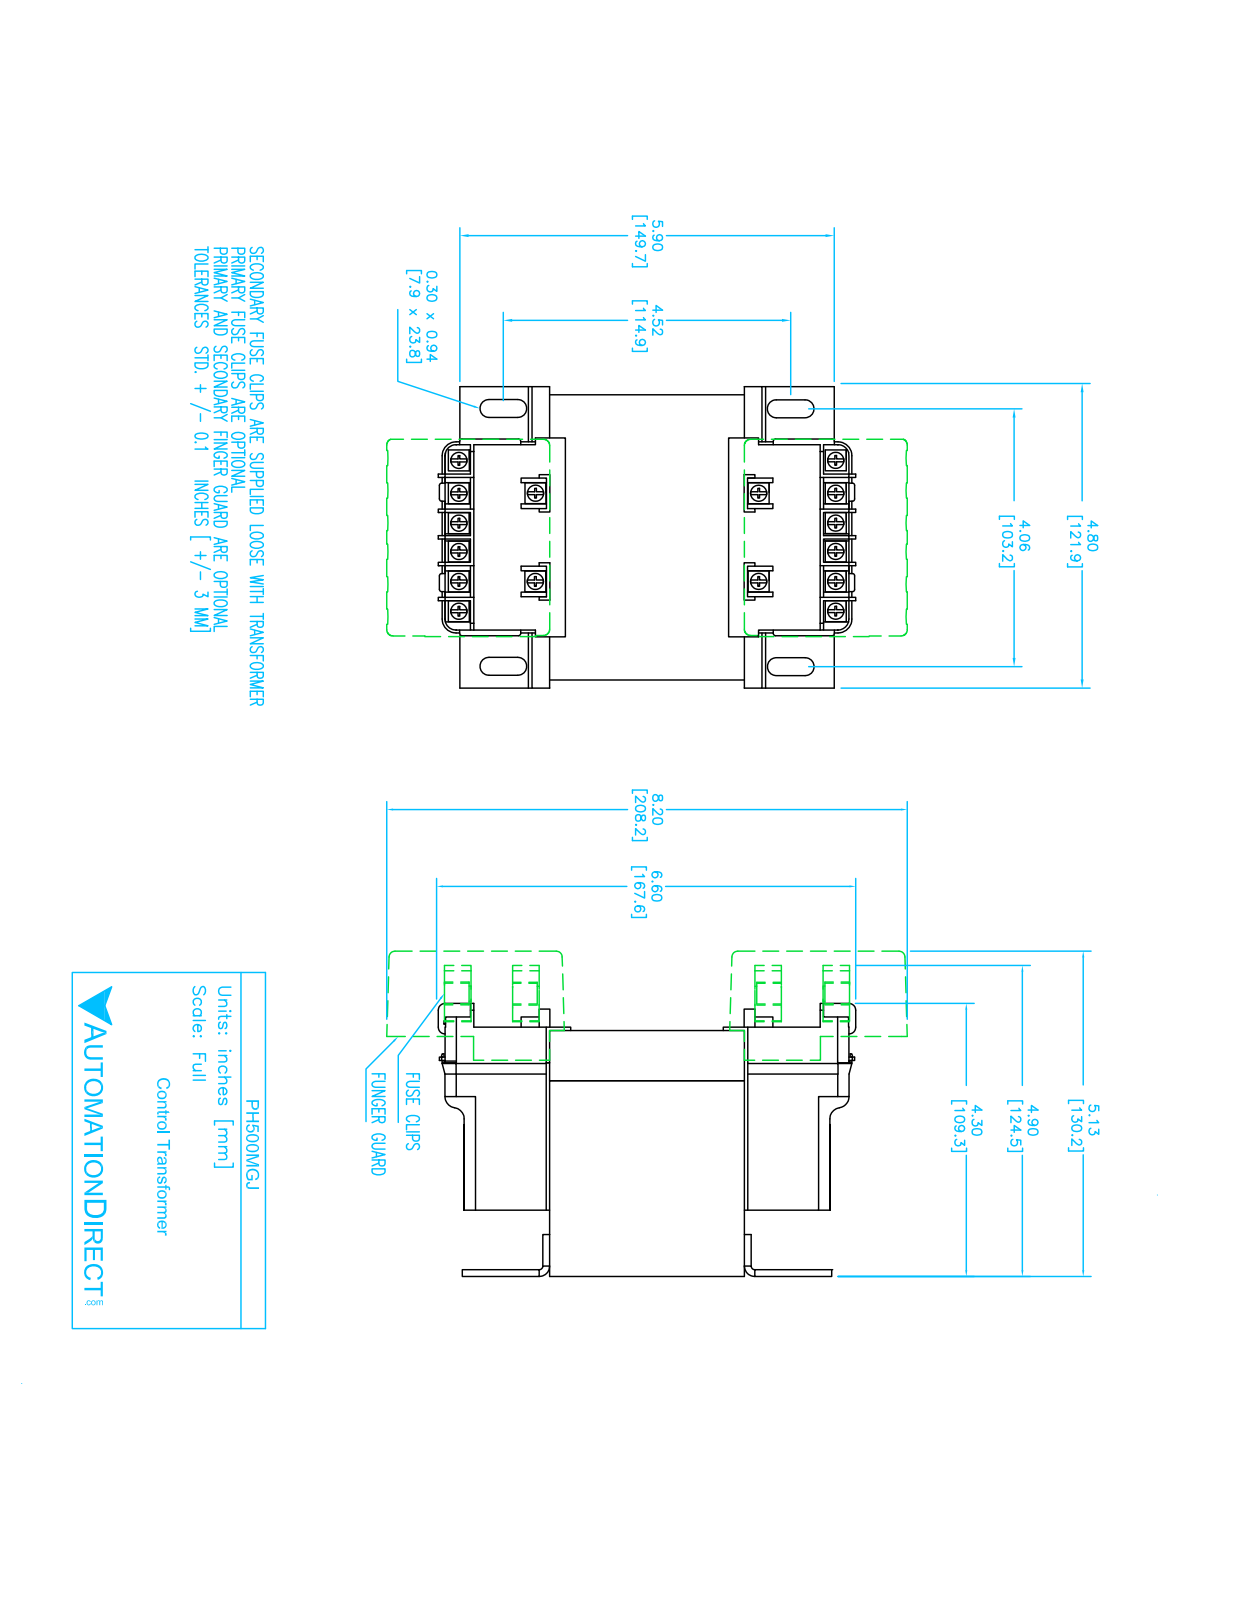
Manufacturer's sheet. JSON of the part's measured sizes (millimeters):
{"part_name": "PH500MGJ", "step_written_by": "SolidWorks 2017 (AUTOMOTIVE_DESIGN)", "units": "millimeters", "bodies": {"solids": 8, "faces": 670, "planar": 394, "cylindrical": 196, "other": 80}, "overall_size": [166.9, 120.7, 107], "volume_mm3": 1438000, "surface_area_mm2": 173700, "round_holes": [[4, 4], [7, 2]], "partial_cylinders_radius": [[1, 86], [5, 18], [3.9, 8], [2.5, 4], [6.2, 4], [1.6, 2], [3.6, 2]], "face_to_face_distances": [78, 76, 80.7, 4.7, 16, 98, 95, 19, 14.2, 31], "hole_center_spacings": [70, 117.9, 137.1, 95]}
